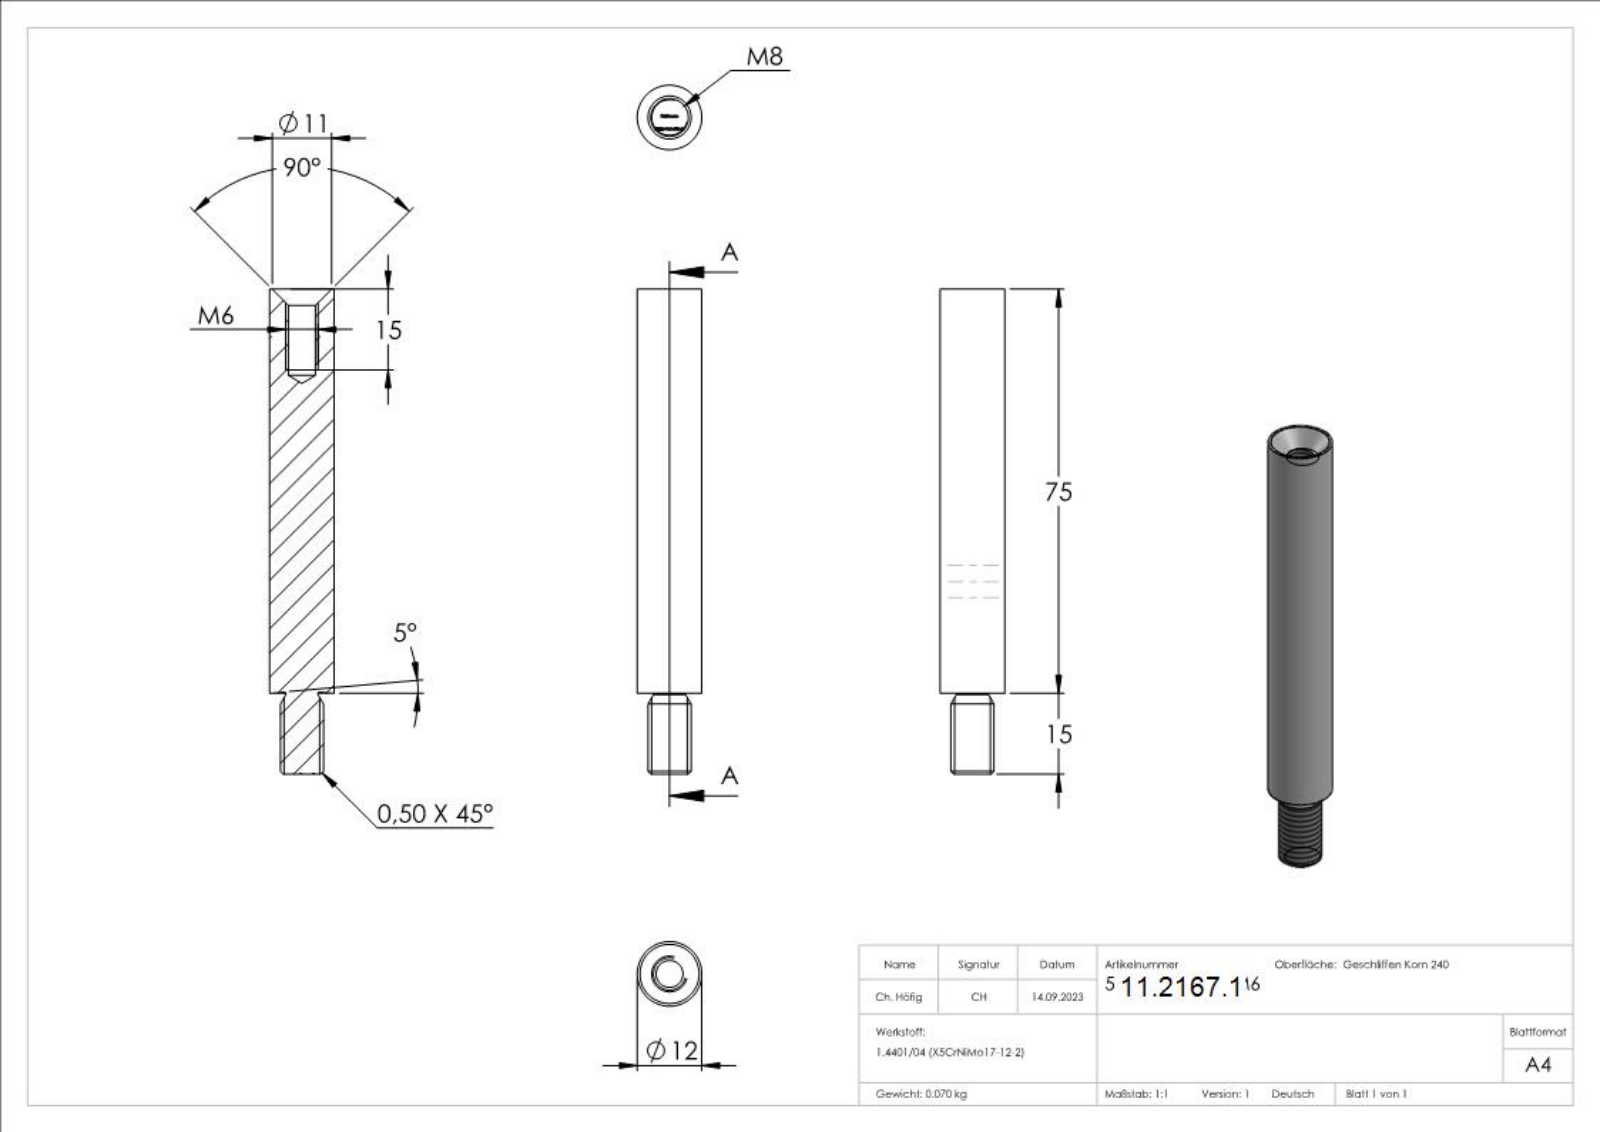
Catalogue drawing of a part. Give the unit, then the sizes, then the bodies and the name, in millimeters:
Units: millimetres
Overall size (bounding box): 90 × 12 × 12
Round holes (diameter × count): ⌀5 ×1
Round bosses / shafts (diameter × count): ⌀12 ×1, ⌀8 ×1
Main face-to-face distances: 90, 89.9, 0.77, 1.29, 2.38, 2.39, 0.72, 1.55, 2.44, 0.57
Volume: 8 775 mm³ · Surface area: 3 690 mm²
Bodies: 1 solid, 269 faces (157 planar, 3 cylindrical, 109 other)
Part name (STEP PRODUCT): 50236-V4A-75-M6
STEP written by: SolidWorks 2018 (CONFIG_CONTROL_DESIGN)
